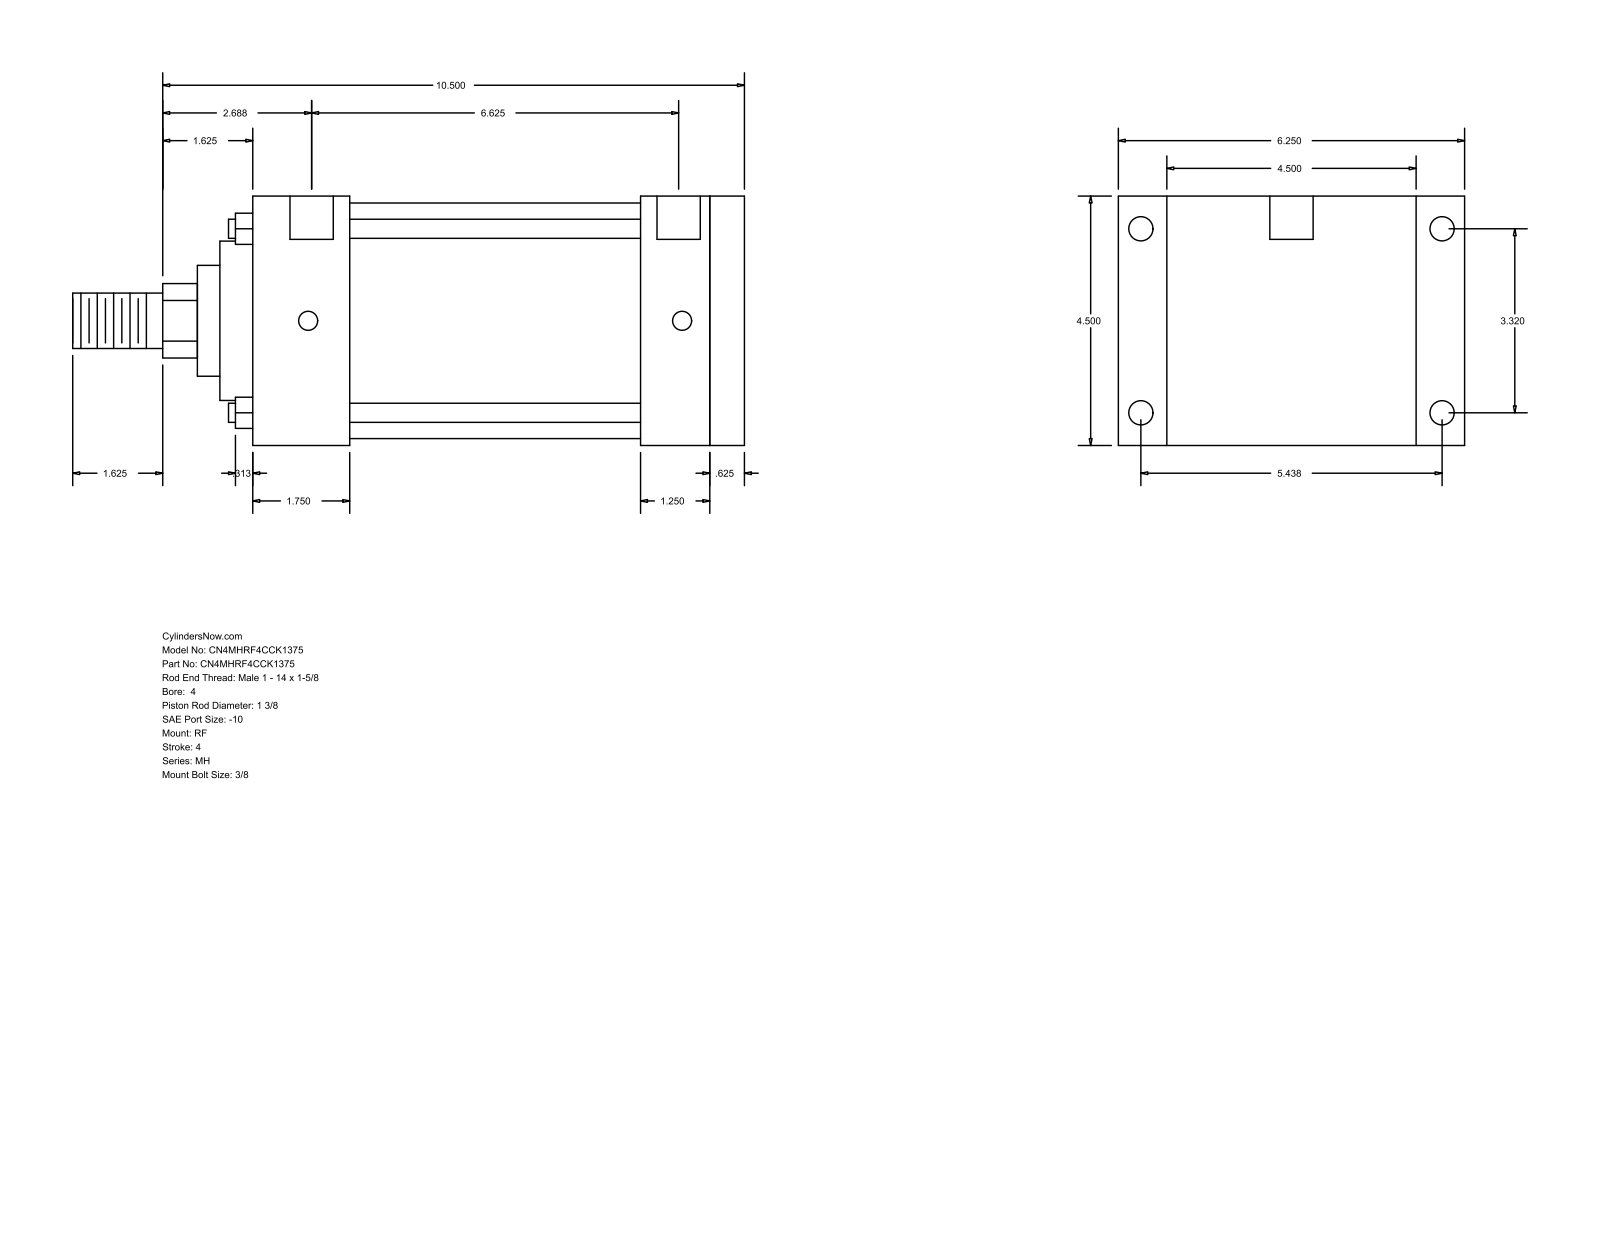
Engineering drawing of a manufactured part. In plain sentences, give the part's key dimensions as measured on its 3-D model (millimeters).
The part is named "MH_RF__0400_1.375". Its 3-D file was written by "GSSL Pune (CONFIG_CONTROL_DESIGN)". It is 0 solids with 94 faces: 65 planar, 29 cylindrical and 0 other. Overall it measures 307.98 by 158.75 by 114.3 millimeters. Round holes: 4 of diameter 8.73, 4 of diameter 11.13, 2 of diameter 19.84. Round bosses or shafts: 4 of diameter 8.76, 1 of diameter 107.95, 1 of diameter 73.03, 1 of diameter 50.8, 1 of diameter 34.92, 1 of diameter 25.4. Partial cylindrical surfaces (rounded edges, fillets, slot ends): 1 of radius 17.06. The main face-to-face distances are 114.3, 225.43, 15.88, 209.55, 44.45, 165.1, 180.98, 177.8, 133.35, 31.75. The hole center spacings are 84.32, 138.12, 161.82, 171.45, 1.58, 1.59, 168.28, 169.86.
